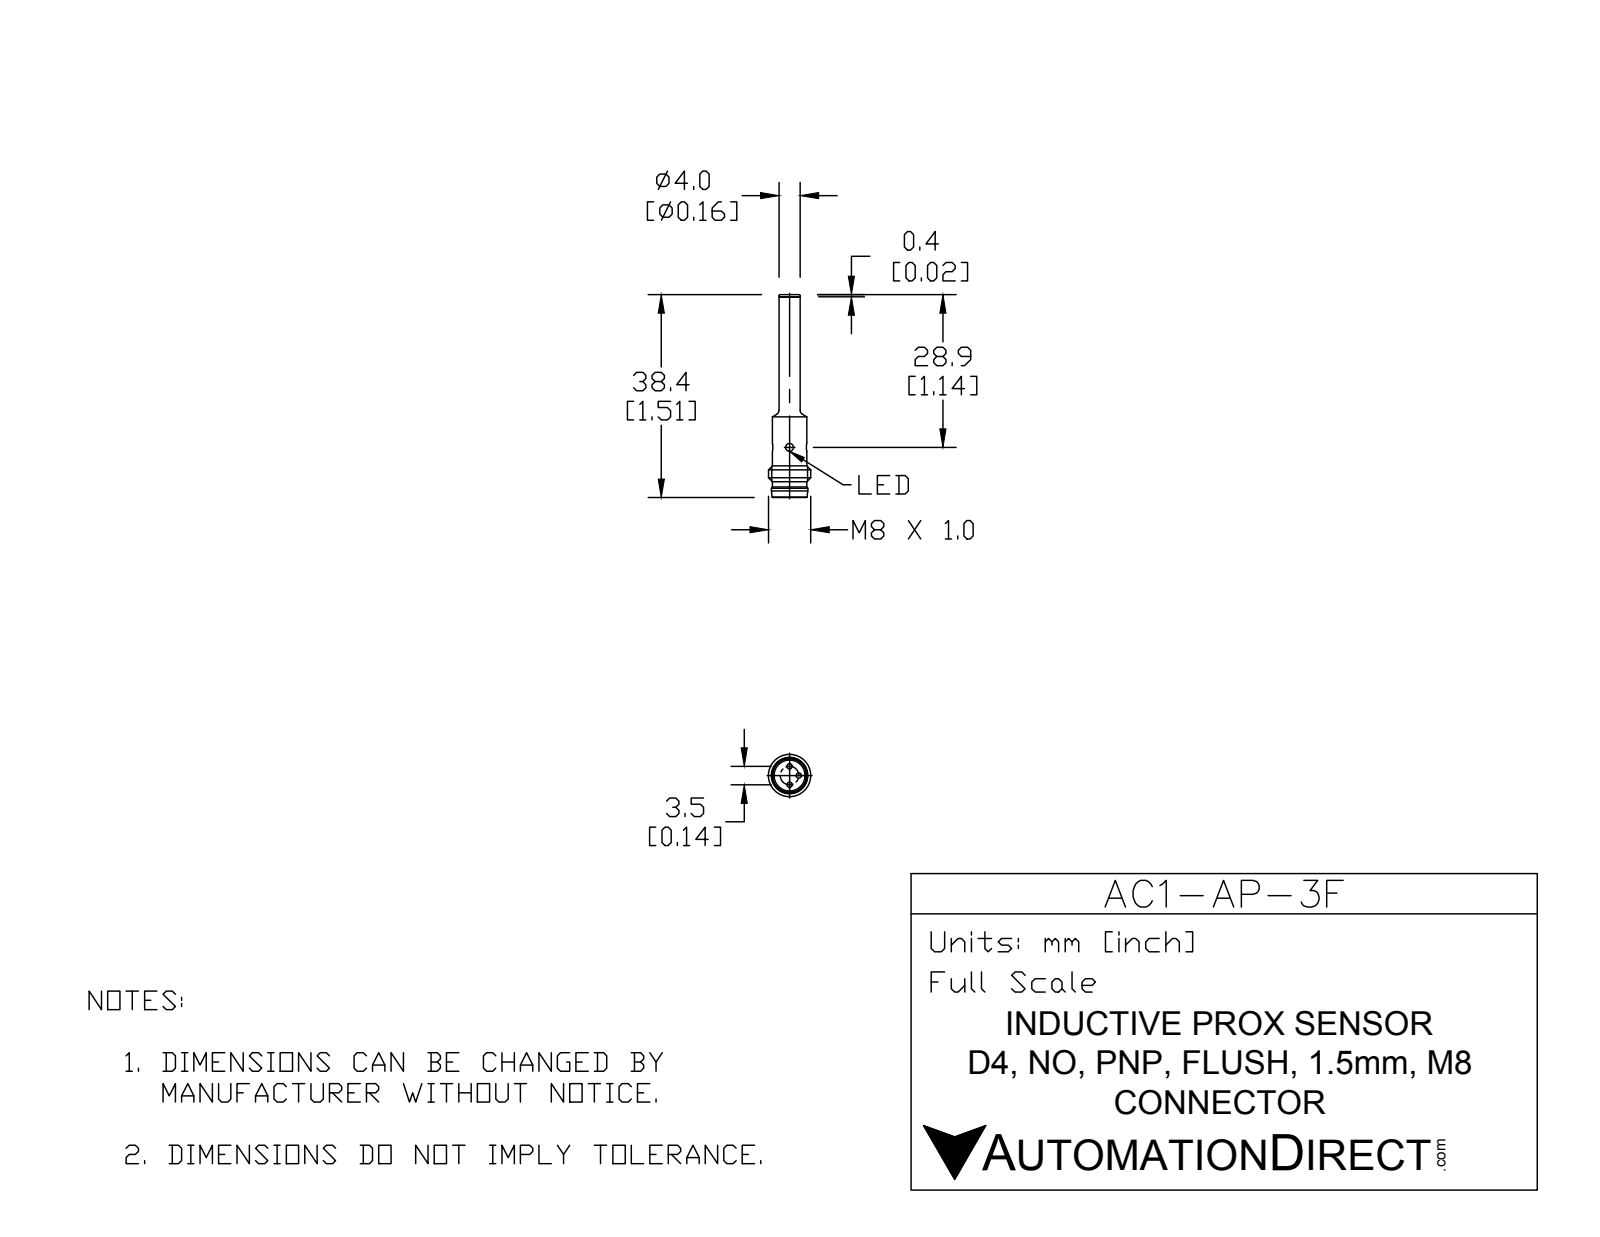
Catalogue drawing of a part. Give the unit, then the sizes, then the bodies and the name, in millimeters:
Units: millimetres
Overall size (bounding box): 38.4 × 8 × 8
Round holes (diameter × count): ⌀1.5 ×2, ⌀5.85 ×1
Round bosses / shafts (diameter × count): ⌀1 ×3, ⌀8 ×1, ⌀6.9 ×1, ⌀6.5 ×1, ⌀4 ×1
Main face-to-face distances: 33.4, 5.5, 5, 38.4, 38, 33, 0.4
Volume: 757 mm³ · Surface area: 840 mm²
Bodies: 4 solids, 59 faces (11 planar, 26 cylindrical, 22 other)
Part name (STEP PRODUCT): AC1-AP-3F
STEP written by: SolidWorks 2015 (CONFIG_CONTROL_DESIGN)
